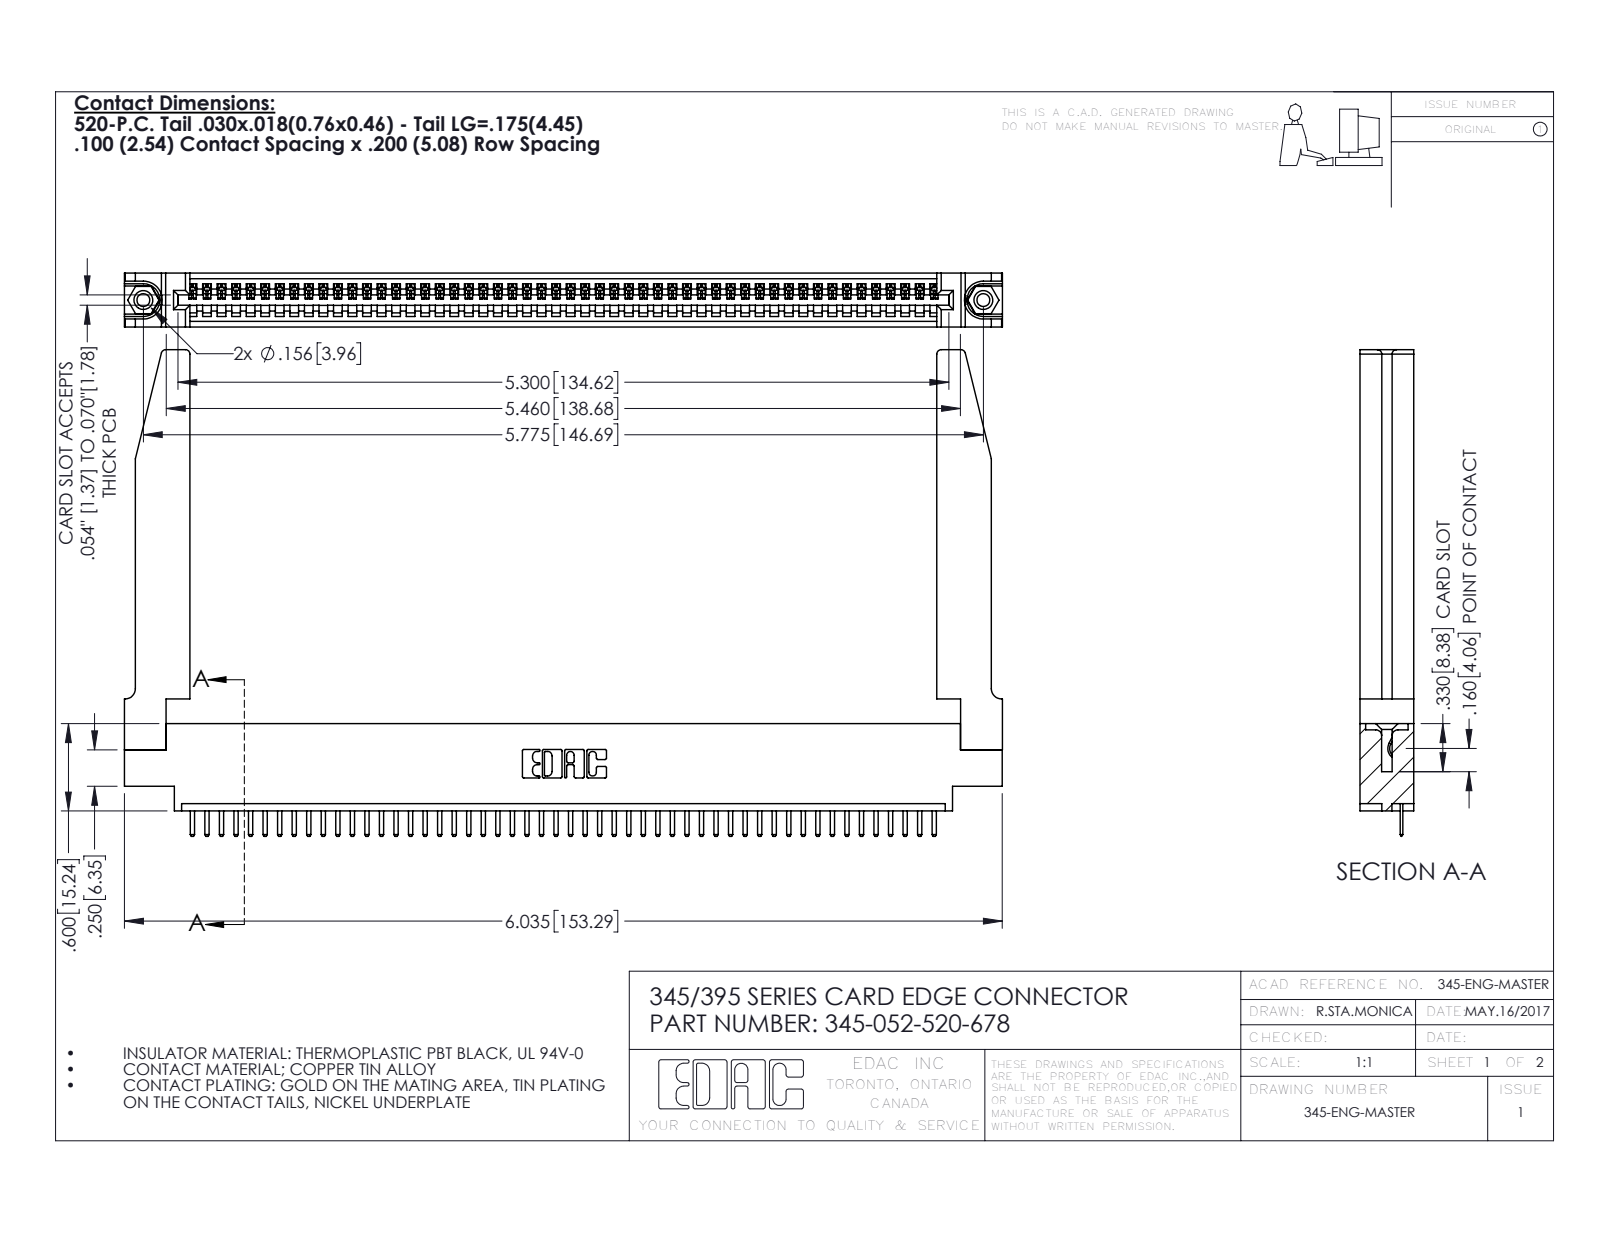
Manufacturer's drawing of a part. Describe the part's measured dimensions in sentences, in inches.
The part is named "345-292-001_345-293-120; 345-250-001_345-250-001-102; 345 Part_0.170 Offset - 0.156 Dia-TH; 345-220-078_345-220-078 (+1 more)". Its 3-D file was written by "SolidWorks 2016 (CONFIG_CONTROL_DESIGN)". It is 57 solids with 3588 faces: 2410 planar, 1126 cylindrical and 52 other. Overall it measures 6.036 by 3.345 by 0.37 inches. Its volume is 1.352 cubic inches and its surface area 39.88 square inches. Round holes: 2 of diameter 0.089, 2 of diameter 0.125, 2 of diameter 0.156, 1 of diameter 0.064. Round bosses or shafts: 2 of diameter 0.155. Partial cylindrical surfaces (rounded edges, fillets, slot ends): 106 of radius 0.01, 104 of radius 0.006, 22 of radius 0.01, 8 of radius 0.03, 6 of radius 0.007, 6 of radius 0.031, 3 of radius 0.026, 2 of radius 0.031. The main face-to-face distances are 0.37, 0.072, 0.298, 0.098, 0.272, 0.025, 0.2, 0.225, 0.15, 0.148. The hole center spacings are 0.27, 5.539, 5.775.
